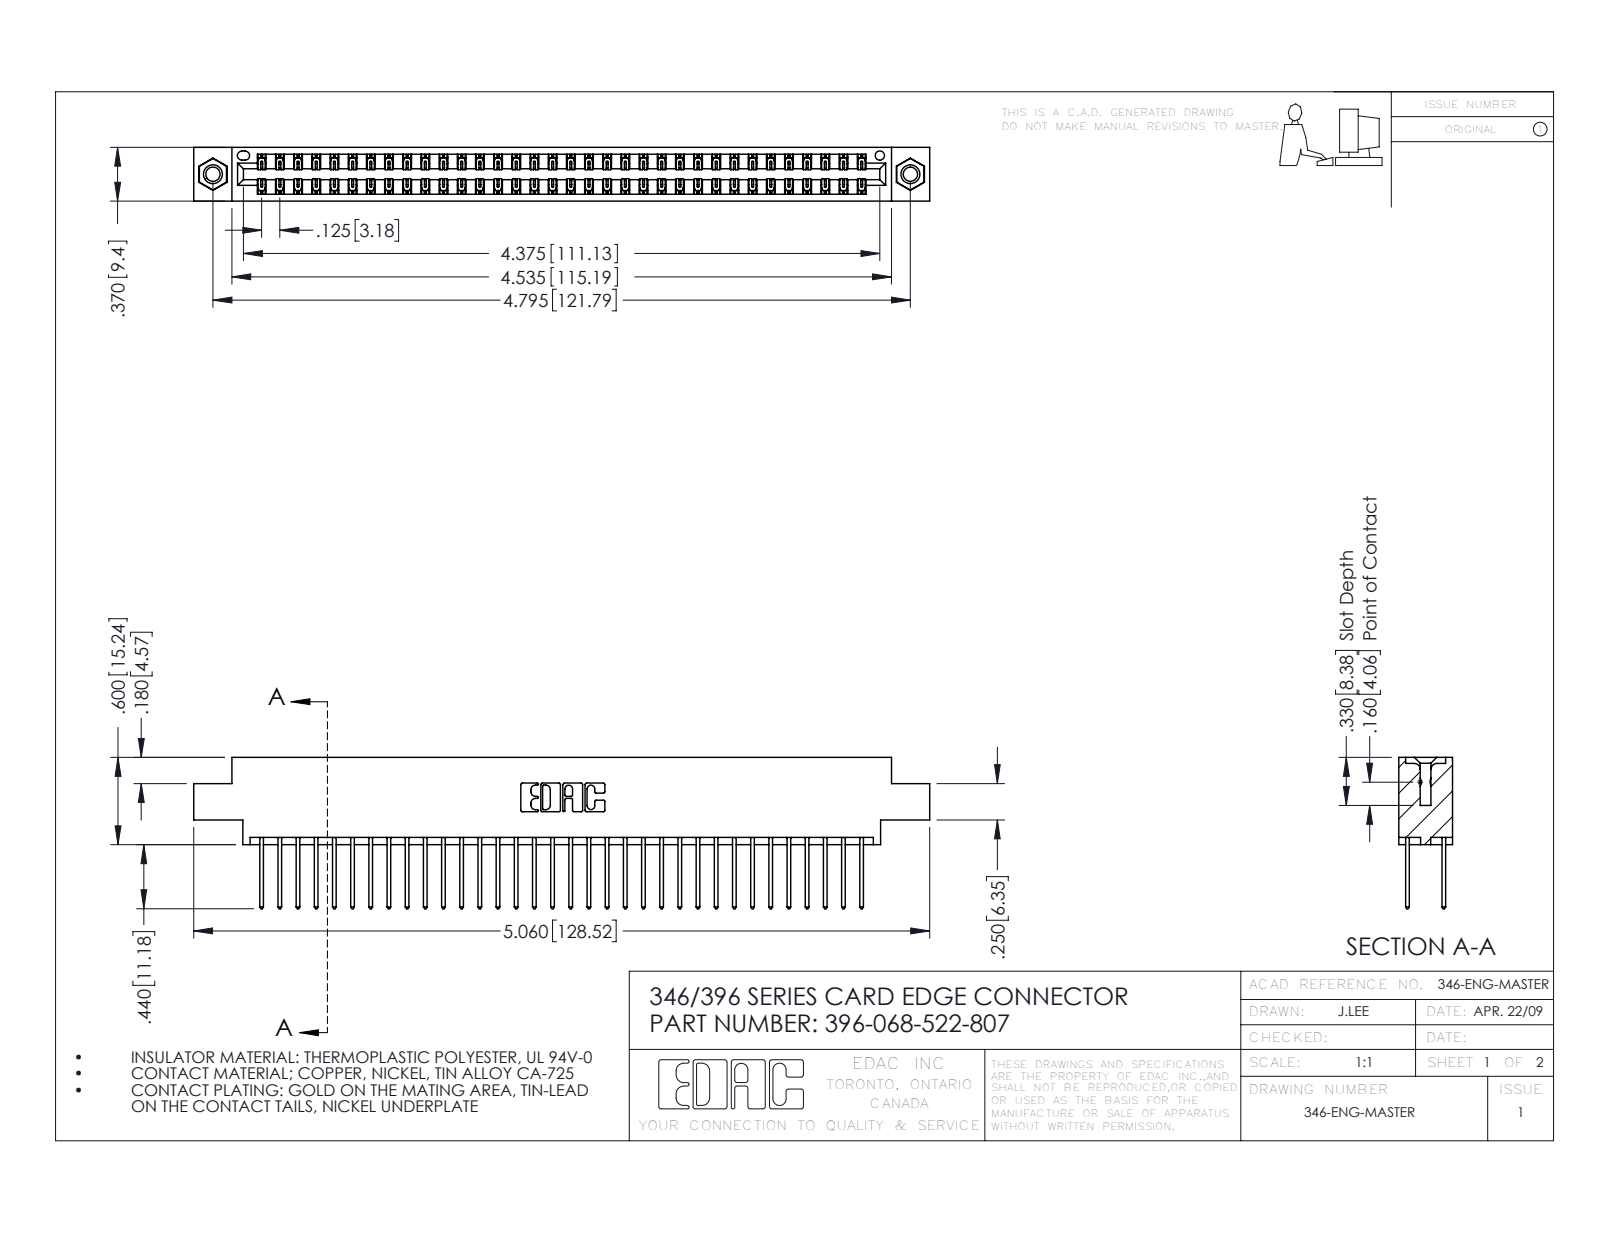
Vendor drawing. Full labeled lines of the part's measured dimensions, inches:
Part name (STEP PRODUCT): 345-292-001_345-293-122; 345-250-001_345-250-005-103; 346 Part_0.170 Offset - 0.156 Dia-TI; 396-068-522-807
STEP written by: SolidWorks 2016 (CONFIG_CONTROL_DESIGN)
Units: inches
Bodies: 71 solids, 3722 faces (2492 planar, 1214 cylindrical, 16 other)
Overall size (bounding box): 5.06 × 1.04 × 0.37
Volume: 0.761 in³ · Surface area: 27.97 in²
Round holes (diameter × count): ⌀0.098 ×2, ⌀0.125 ×2, ⌀0.156 ×2, ⌀0.064 ×1
Round bosses / shafts (diameter × count): ⌀0.155 ×2
Partial cylindrical surfaces — rounded edges, fillets, slot ends (radius × count): R0.006 ×102, R0.01 ×68, R0.01 ×22, R0.007 ×6, R0.031 ×6, R0.026 ×3, R0.014 ×2, R0.022 ×2
Main face-to-face distances: 0.048, 0.322, 0.25, 0.37, 0.072, 0.298, 0.025, 0.275, 0.222, 0.148
Hole centre spacings: 0.246, 4.587, 4.795
